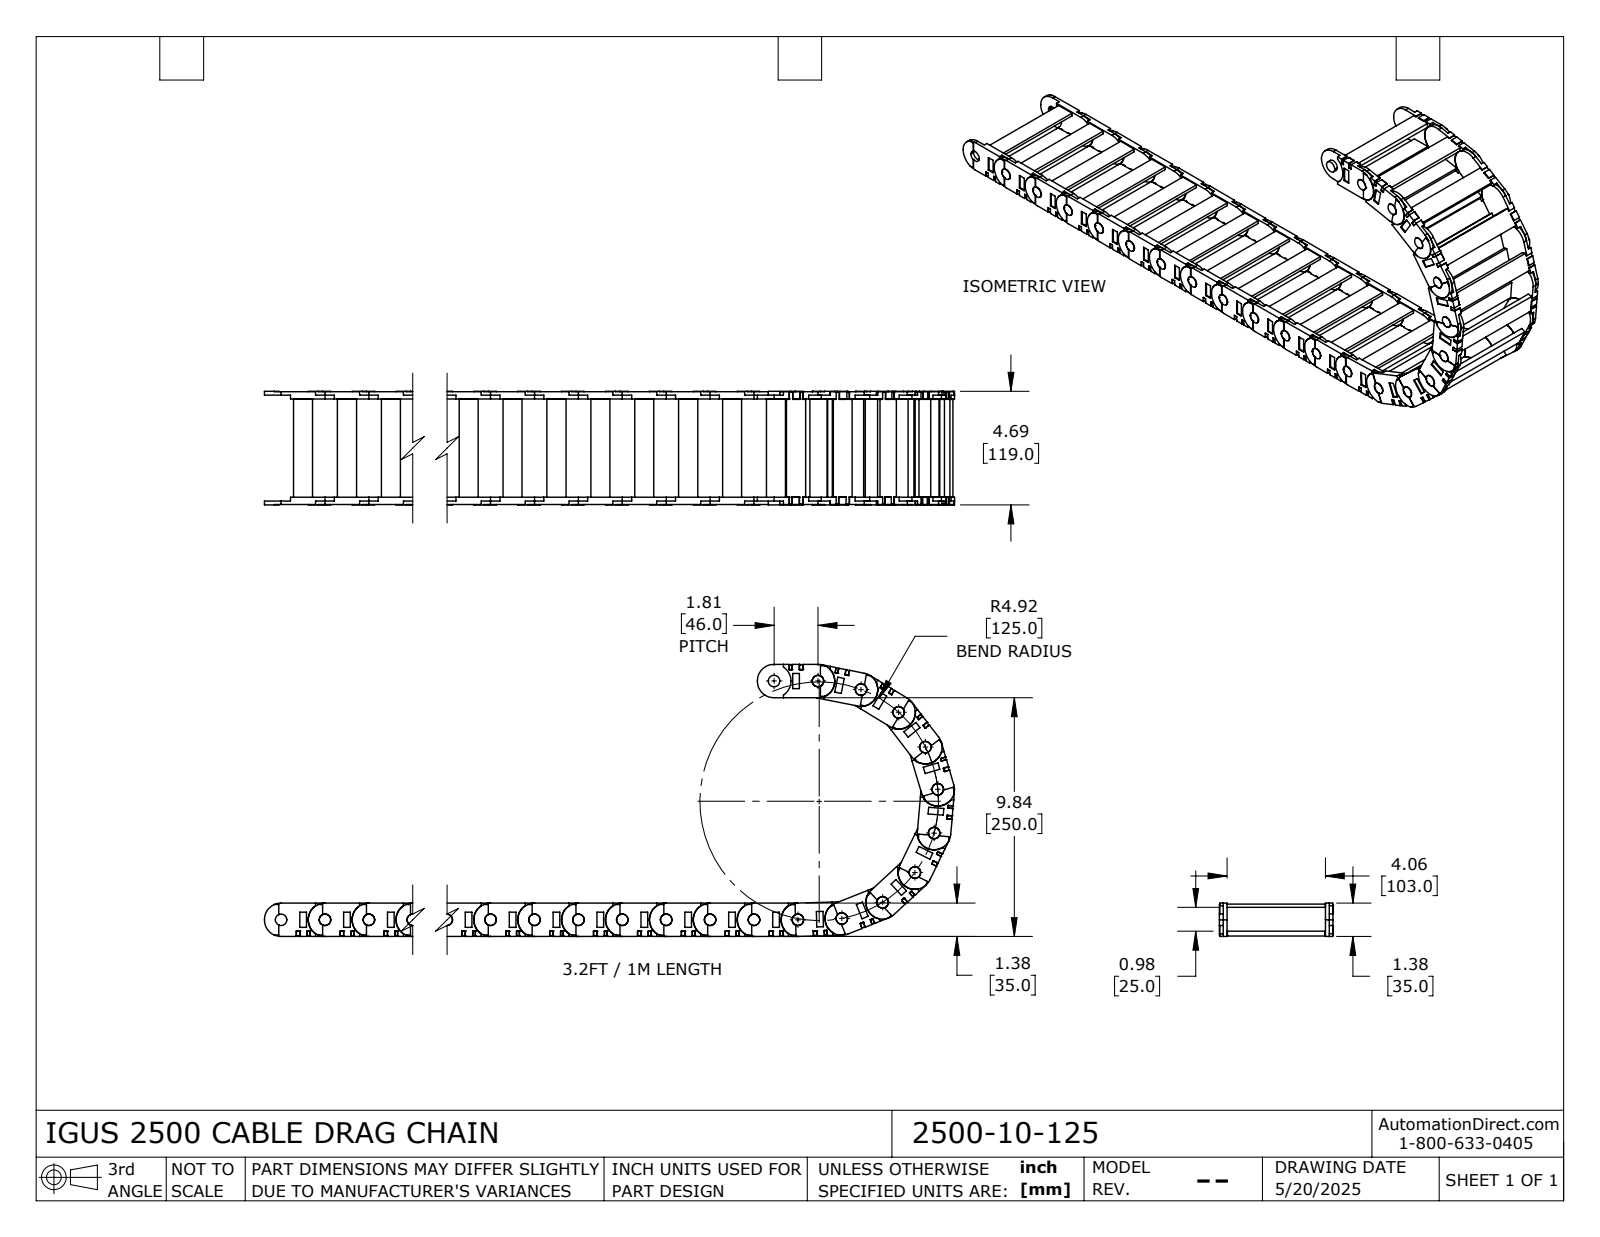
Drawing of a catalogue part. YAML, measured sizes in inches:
part_name: "2500_10_125"
step_written_by: "SolidWorks 2024 (AUTOMOTIVE_DESIGN)"
units: inches
bodies: {solids: 66, faces: 2398, planar: 1870, cylindrical: 528, other: 0}
overall_size: [28.879, 11.22, 4.685]
volume: 55.55
surface_area: 815.8
round_holes:
  - {diameter: 0.473, count: 22}
round_bosses_or_shafts:
  - {diameter: 0.472, count: 22}
  - {diameter: 1.378, count: 21}
partial_cylinders:
  - {radius: 0.697, count: 23}
  - {radius: 0.689, count: 2}
face_to_face_distances: [0.157, 4.213, 4.37, 0.134, 0.197, 0.142, 0.299, 4.354, 4.512, 0.984]
hole_center_spacings: [1.811, 3.622, 5.433, 7.244, 9.055, 10.866, 12.677, 3.56]
